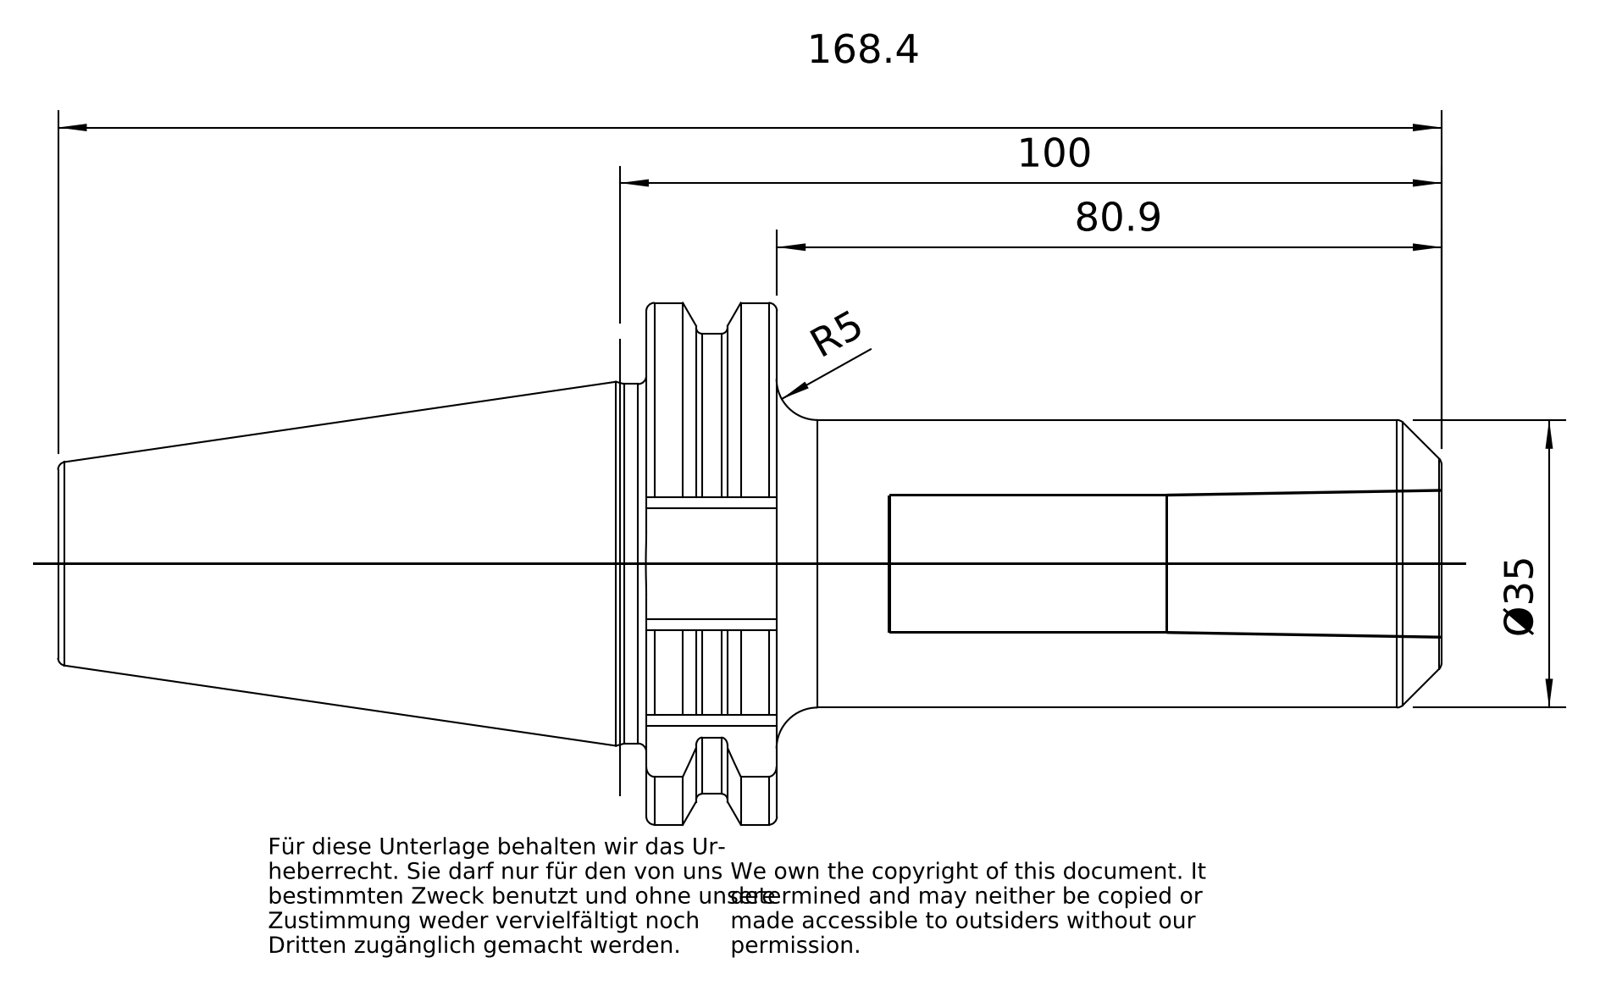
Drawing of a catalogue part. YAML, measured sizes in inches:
part_name: "40-421-02"
step_written_by: "PRO/ENGINEER BY PARAMETRIC TECHNOLOGY CORPORATION, 2010430 (CONFIG_CONTROL_DESIGN)"
units: inches
bodies: {solids: 1, faces: 101, planar: 21, cylindrical: 28, other: 52}
overall_size: [6.624, 2.501, 2.418]
volume: 10.24
surface_area: 49.3
round_holes:
  - {diameter: 0.545, count: 1}
  - {diameter: 0.658, count: 1}
  - {diameter: 0.67, count: 1}
  - {diameter: 0.689, count: 1}
round_bosses_or_shafts:
  - {diameter: 1.722, count: 1}
  - {diameter: 1.378, count: 1}
  - {diameter: 0.63, count: 1}
partial_cylinders:
  - {radius: 0.053, count: 5}
  - {radius: 1.102, count: 1}
  - {radius: 1.25, count: 1}
face_to_face_distances: [0.624, 1.165, 0.541, 1.866, 3.811, 3.187, 2.646, 0.638, 2.813, 3.437]
